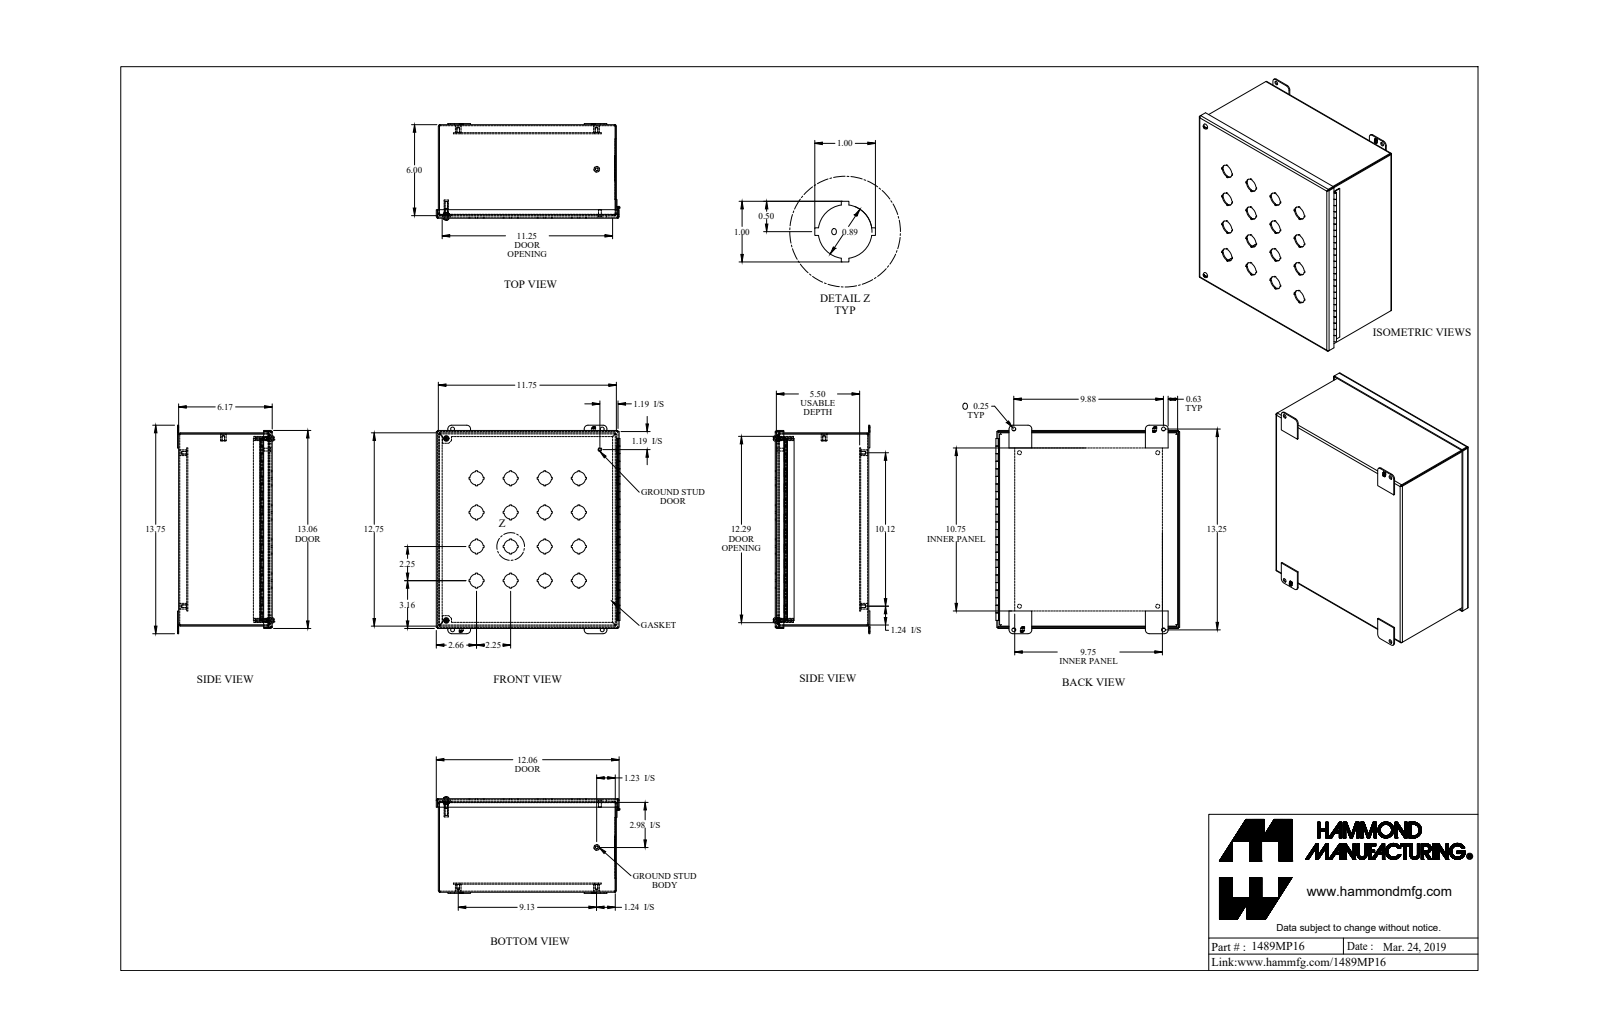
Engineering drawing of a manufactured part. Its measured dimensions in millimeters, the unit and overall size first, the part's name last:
Units: millimetres
Overall size (bounding box): 349.3 × 307.9 × 161.8
Round holes (diameter × count): ⌀22.5 ×16, ⌀6.4 ×6, ⌀4 ×5, ⌀6.7 ×4, ⌀4 ×2, ⌀10.3 ×2
Round bosses / shafts (diameter × count): ⌀9.5 ×5, ⌀9.9 ×2, ⌀7 ×2, ⌀4.8 ×2, ⌀3.8 ×2, ⌀6.4 ×1, ⌀4.8 ×1, ⌀4.4 ×1
Partial cylindrical surfaces — rounded edges, fillets, slot ends (radius × count): R0.9 ×12, R2.7 ×12, R6.4 ×8, R4.1 ×2, R4.3 ×2
Main face-to-face distances: 1.8, 154.9, 141.4, 13.5, 156.8, 296.6, 1.8, 153.1, 322, 15.3
Hole centre spacings: 57.2, 127.8, 80.8, 114.3, 180.7, 161.6, 171.5, 206.1
Volume: 981 100 mm³ · Surface area: 1 035 000 mm²
Bodies: 21 solids, 985 faces (681 planar, 246 cylindrical, 58 other)
Part name (STEP PRODUCT): 1489MP16_Default
STEP written by: SolidWorks 2019 (CONFIG_CONTROL_DESIGN)
